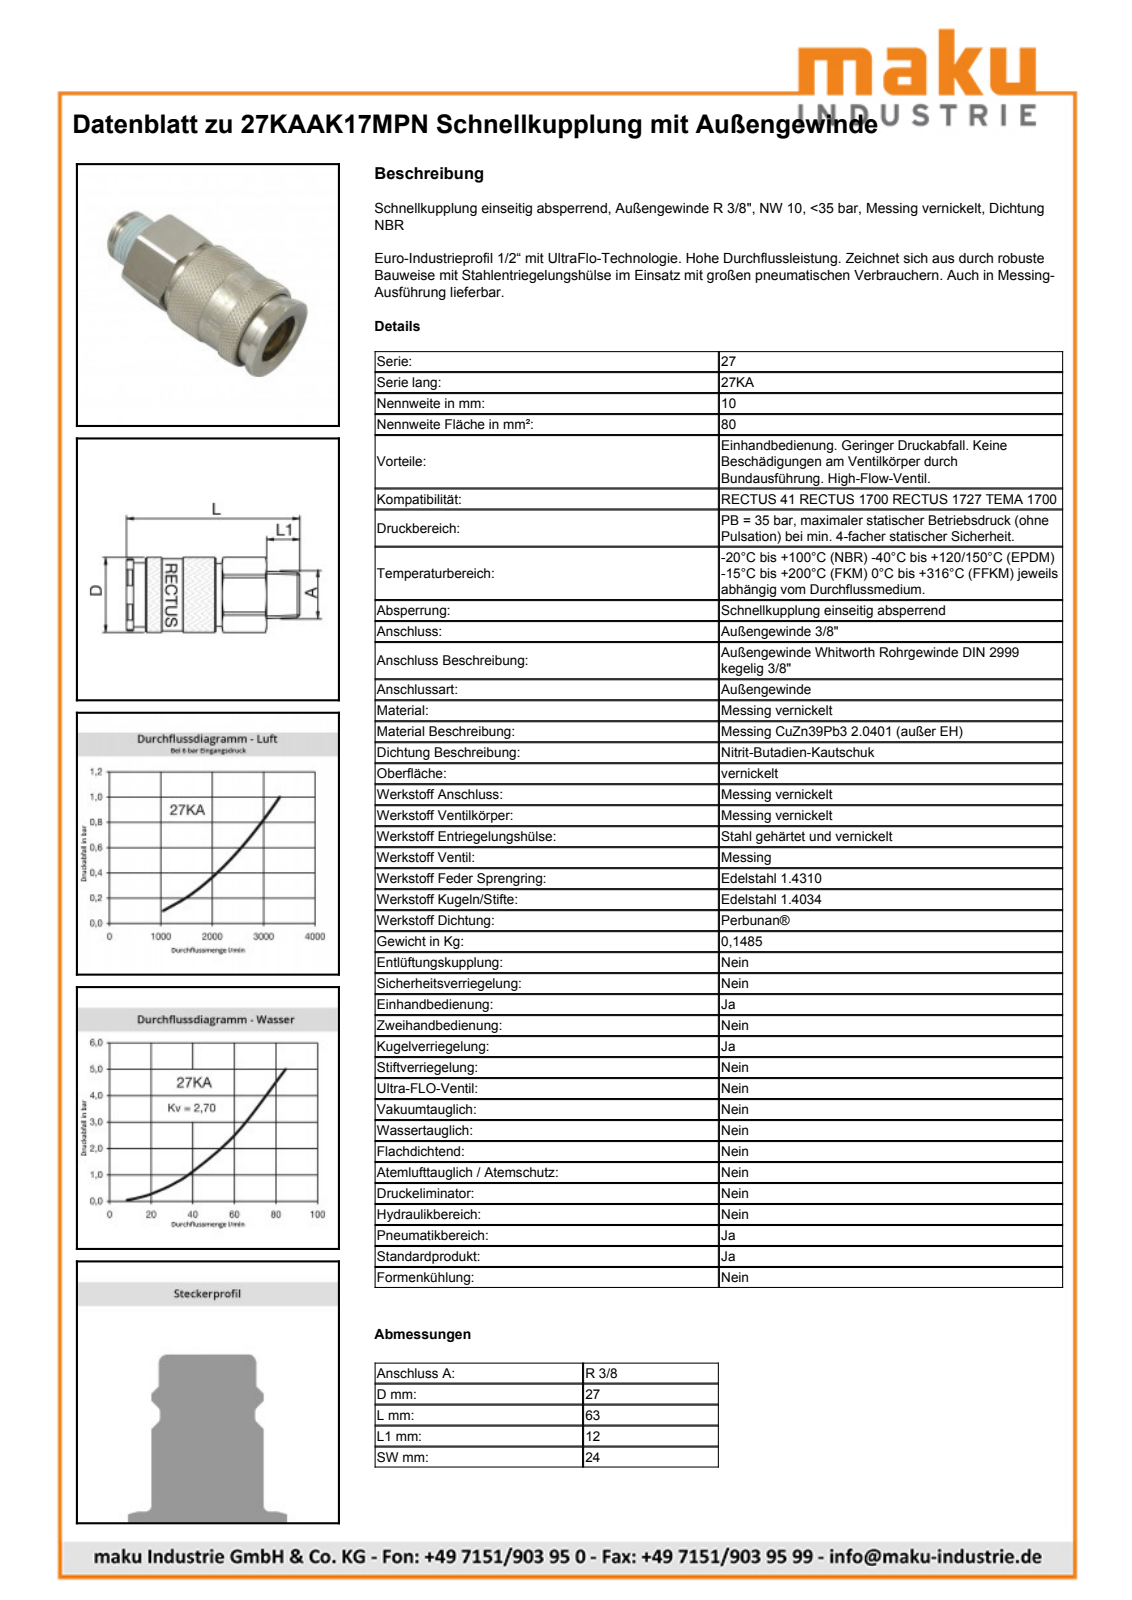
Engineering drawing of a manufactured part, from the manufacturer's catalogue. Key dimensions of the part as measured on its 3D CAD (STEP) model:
Part name (STEP PRODUCT): D113600
STEP written by: Autodesk Inventor 2013 (AUTOMOTIVE_DESIGN)
Units: millimetres
Bodies: 2 solids, 661 faces (228 planar, 83 cylindrical, 350 other)
Overall size (bounding box): 62.55 × 27.15 × 27.15
Volume: 26 884 mm³ · Surface area: 10 711 mm²
Round holes (diameter × count): ⌀19 ×1, ⌀20.3 ×1, ⌀20.95 ×1, ⌀23.35 ×1, ⌀23.55 ×1
Round bosses / shafts (diameter × count): ⌀27.15 ×1, ⌀26 ×1, ⌀23.1 ×1, ⌀22.75 ×1, ⌀20 ×1, ⌀18.8 ×1, ⌀18.7 ×1, ⌀18.64 ×1
Partial cylindrical surfaces — rounded edges, fillets, slot ends (radius × count): R9.9 ×1, R12.9 ×1, R13.53 ×1
Main face-to-face distances: 24, 50.55, 23.98, 12, 62.55, 32.3, 18.25, 30.25, 6.8, 25.5
